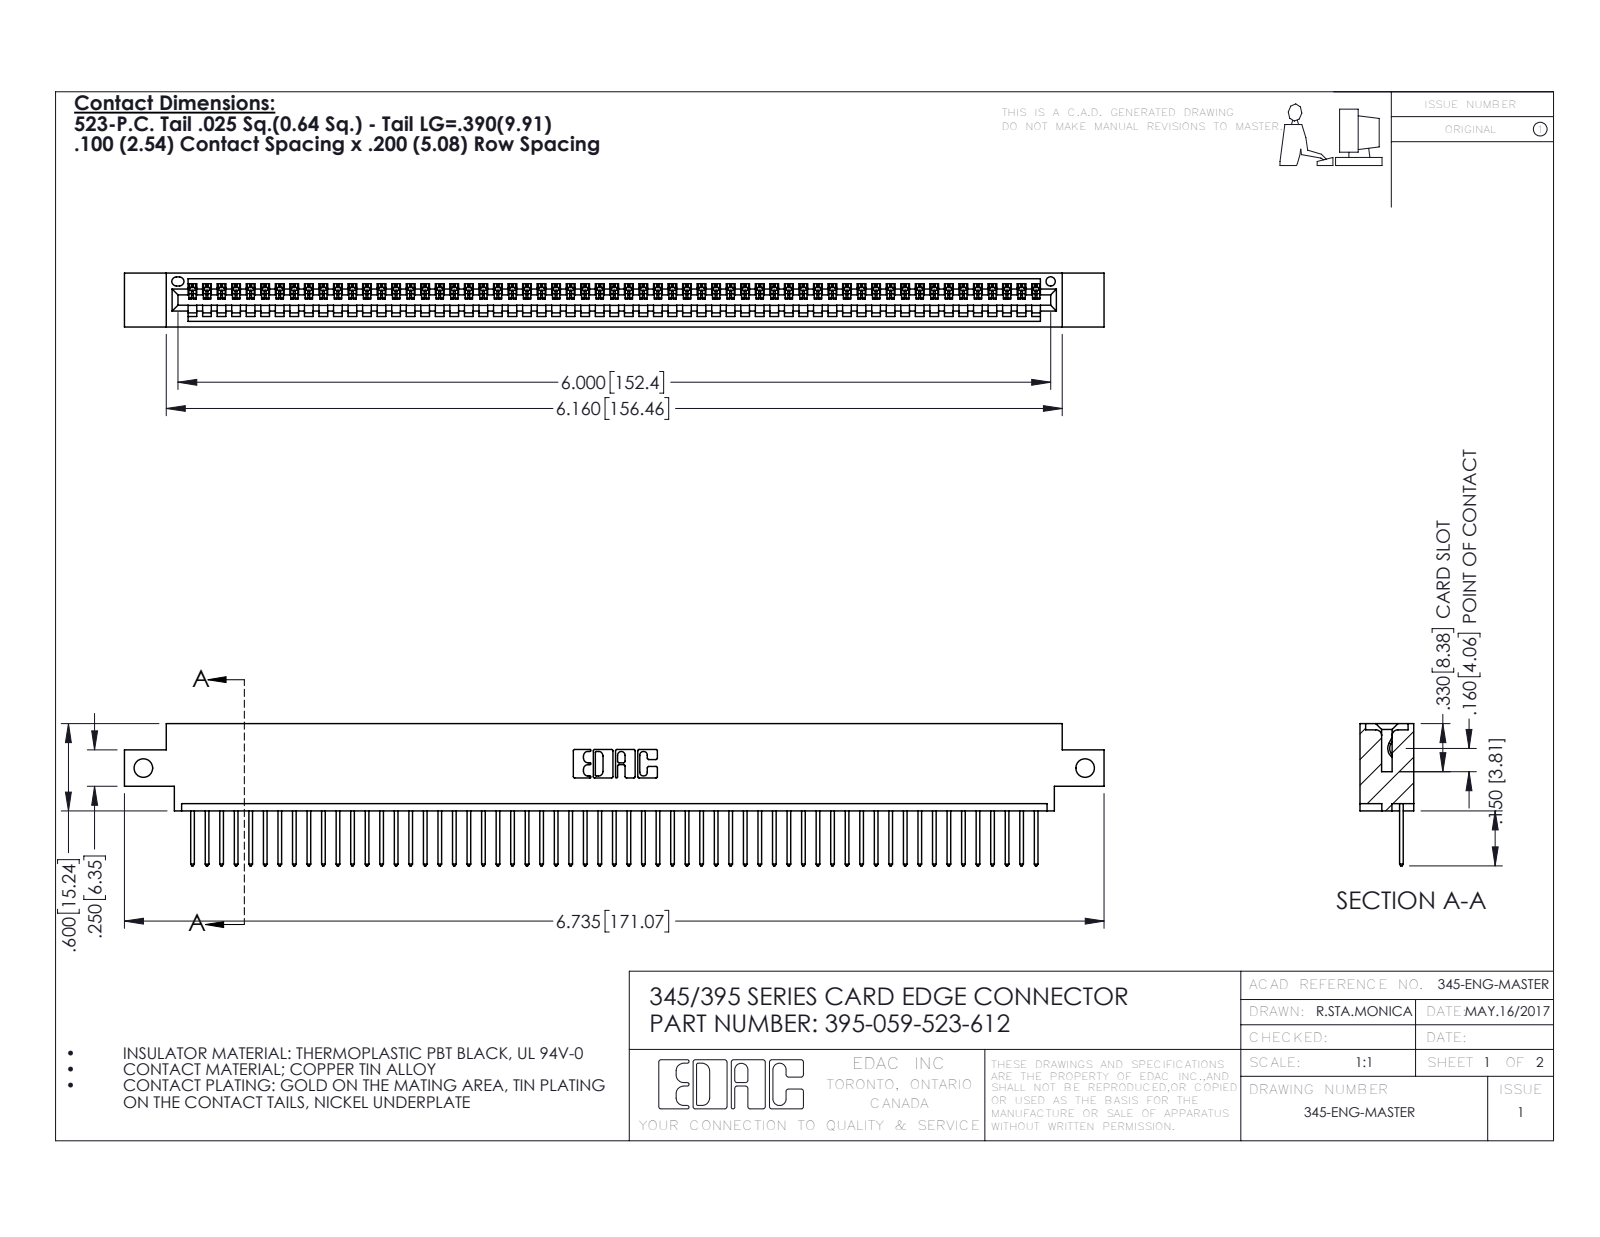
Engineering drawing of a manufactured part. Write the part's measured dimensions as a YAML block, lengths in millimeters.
part_name: "345-292-001_345-293-123; 345 Part_0.170 Offset - Side Mount; 395-059-523-612"
step_written_by: "SolidWorks 2016 (CONFIG_CONTROL_DESIGN)"
units: millimeters
bodies: {solids: 60, faces: 3552, planar: 2444, cylindrical: 1108, other: 0}
overall_size: [171.1, 24.8, 9.4]
volume: 16200
surface_area: 21760
round_holes:
  - {diameter: 3.3, count: 2}
  - {diameter: 1.6, count: 1}
partial_cylinders:
  - {radius: 0.2, count: 118}
  - {radius: 0.3, count: 118}
  - {radius: 0.3, count: 22}
  - {radius: 0.2, count: 6}
  - {radius: 0.8, count: 6}
  - {radius: 0.7, count: 3}
  - {radius: 0.8, count: 2}
  - {radius: 1, count: 2}
face_to_face_distances: [7.6, 1.8, 9.4, 2.5, 6.9, 0.6, 5.1, 5.7, 4.4, 3.8]
hole_center_spacings: [164.5]
